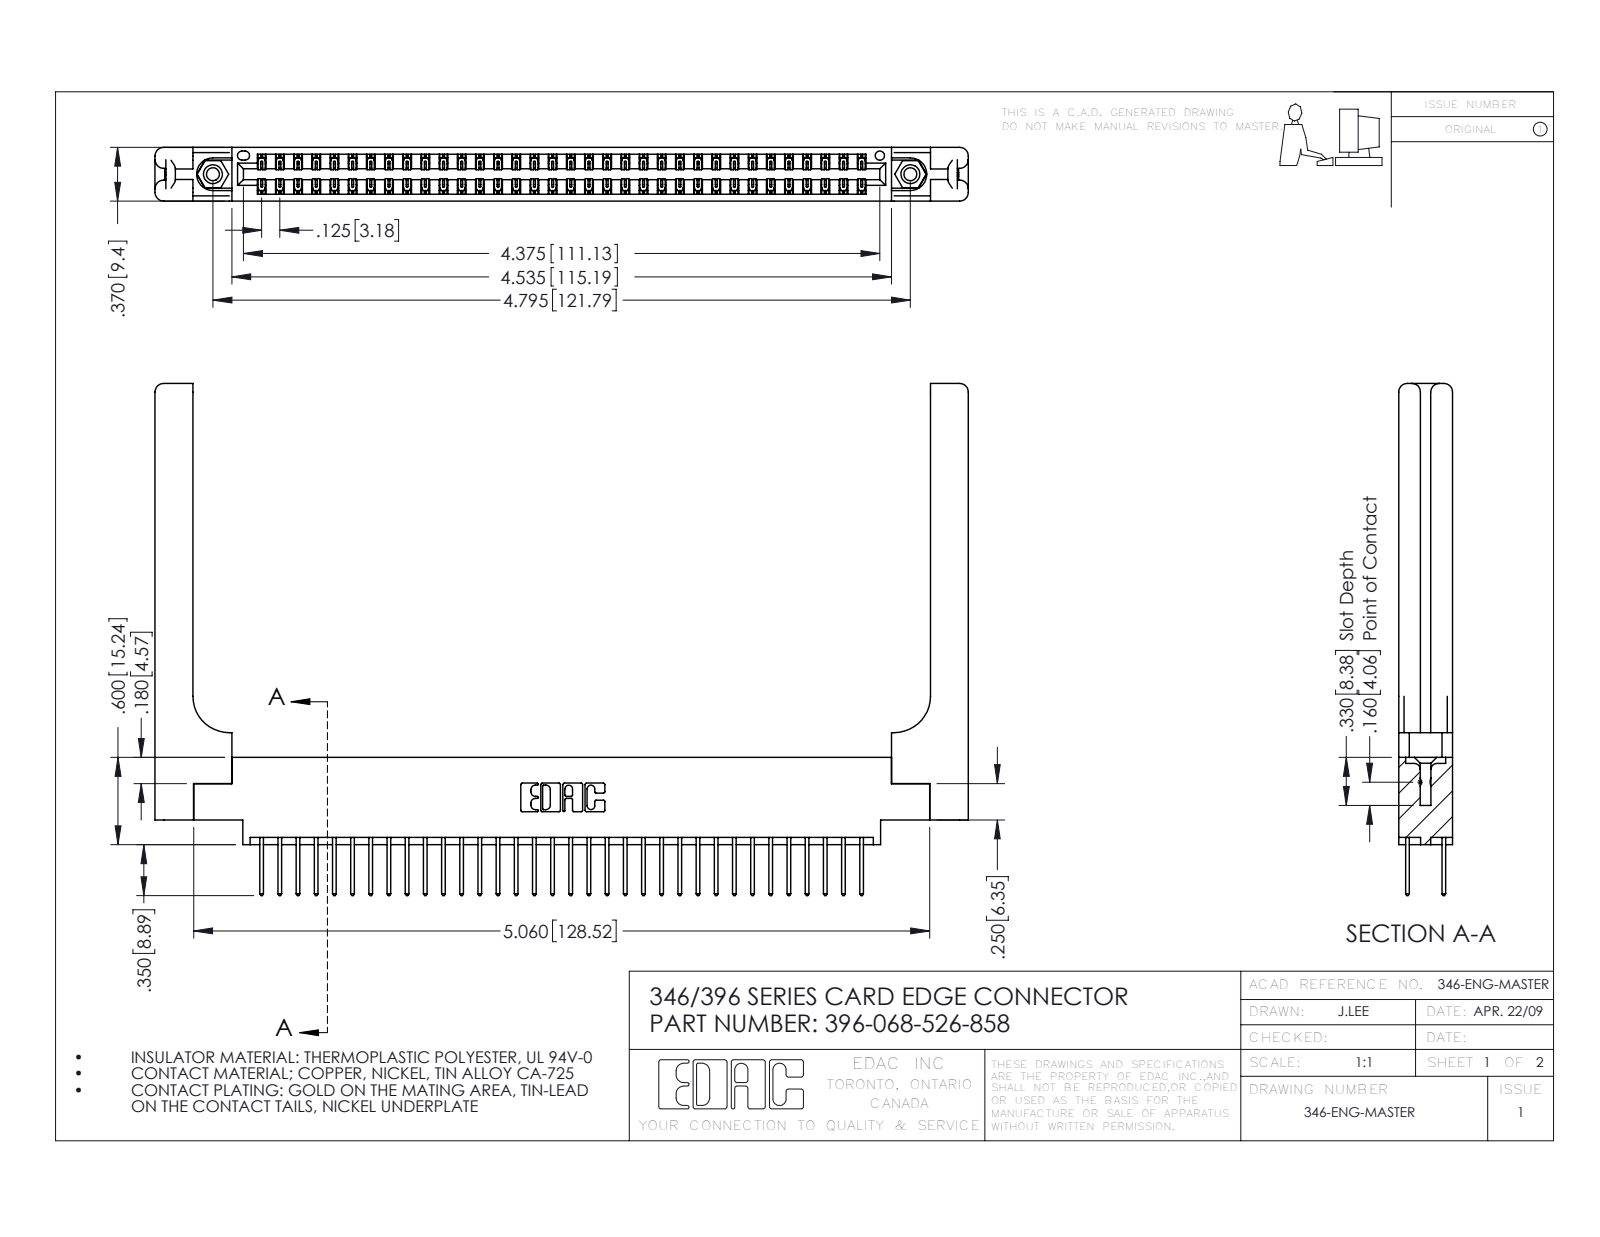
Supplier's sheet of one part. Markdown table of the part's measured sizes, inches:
| quantity | value |
| --- | --- |
| part name | 345-292-001_345-293-126; 345-250-001_345-250-001-102; 346 Part_0.170 Offset - 0.156 Dia-TH; 346-220-058_345-220-058 (+1 more) |
| STEP written by | SolidWorks 2016 (CONFIG_CONTROL_DESIGN) |
| units | inches |
| bodies | 73 solids, 3918 faces (2608 planar, 1250 cylindrical, 60 other) |
| overall size | 5.591 × 3.52 × 0.37 |
| volume | 1.296 in³ |
| surface area | 37.84 in² |
| round holes (diameter × count) | 0.089 × 2, 0.125 × 2, 0.156 × 2, 0.064 × 1 |
| round bosses / shafts (diameter × count) | 0.155 × 2 |
| partial cylindrical surfaces (radius × count) | 0.006 × 102, 0.01 × 68, 0.01 × 22, 0.06 × 16, 0.007 × 6, 0.031 × 6, 0.026 × 3, 0.014 × 2 |
| main face-to-face distances | 0.37, 0.048, 0.322, 0.072, 0.25, 0.148, 0.15, 0.025, 0.298, 0.275 |
| hole center spacings | 0.246, 4.587, 4.795 |
